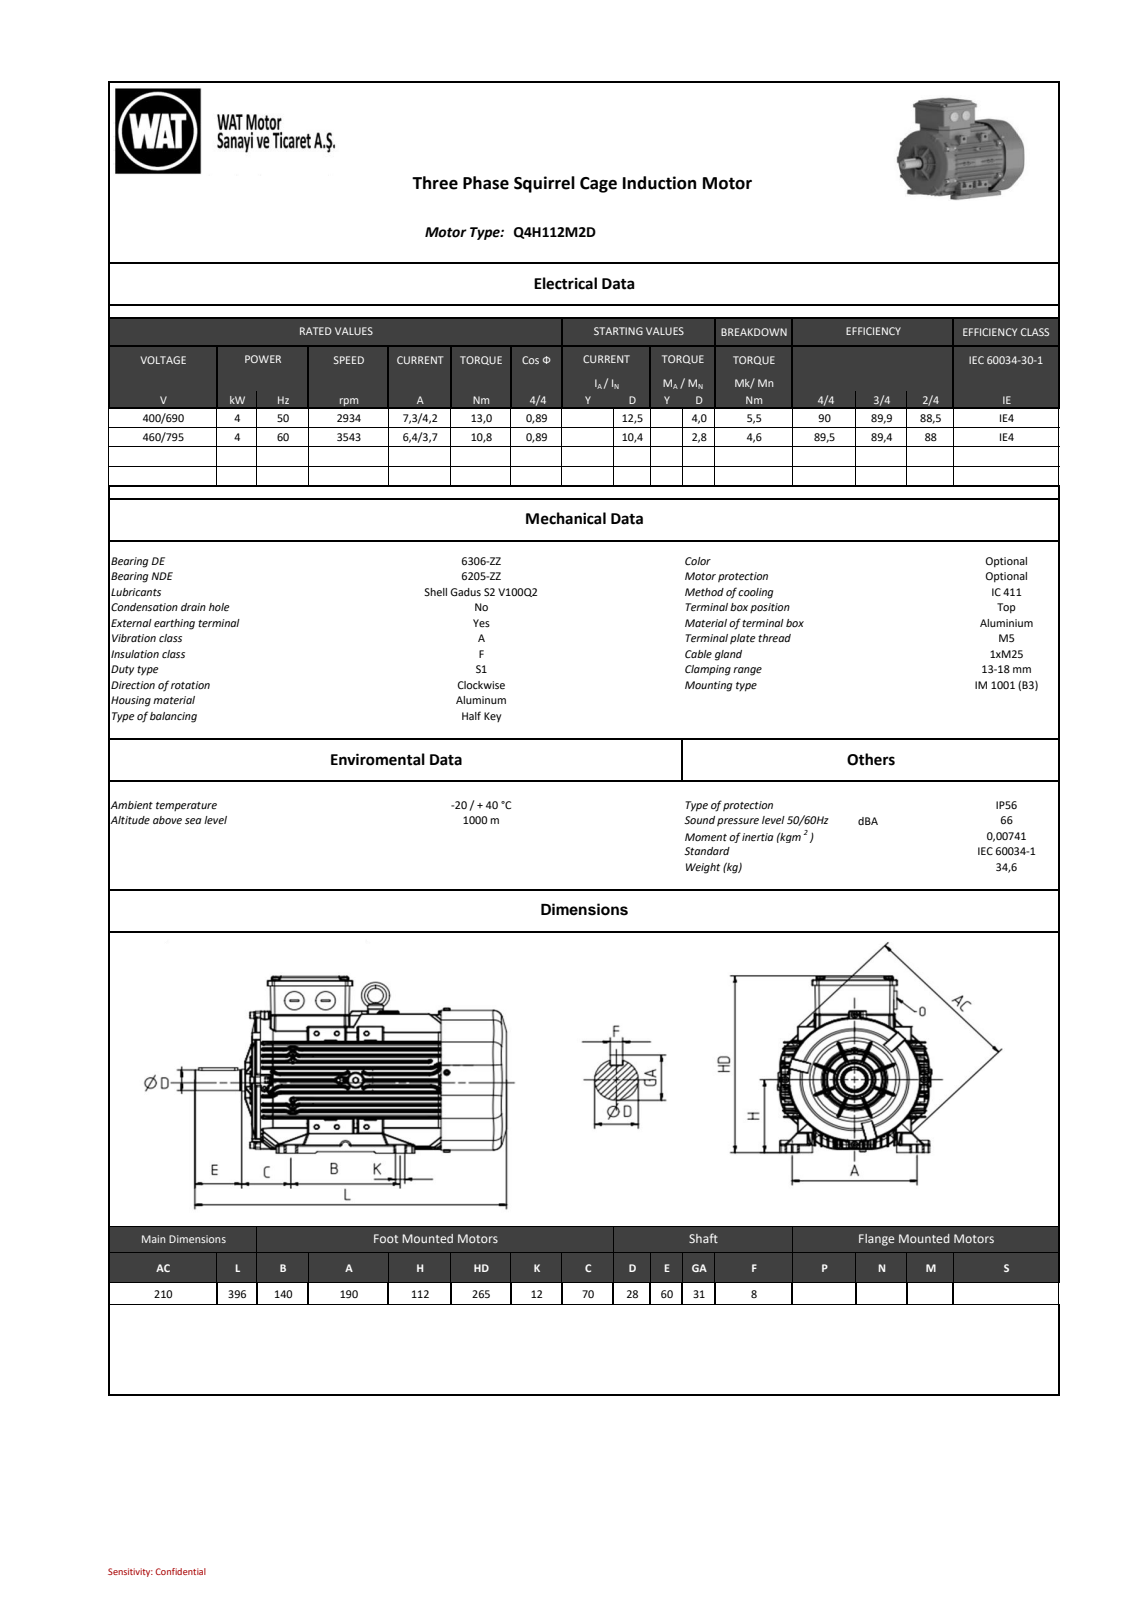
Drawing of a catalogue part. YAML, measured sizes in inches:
part_name: "QH series_ 112_B3_stp_objects"
step_written_by: "SIEMENS PLM Software NX2206.8101 (AUTOMOTIVE_DESIGN)"
units: inches
bodies: {solids: 0, faces: 6868, planar: 1512, cylindrical: 2655, other: 2701}
overall_size: [15.591, 10.807, 8.863]
round_holes:
  - {diameter: 0.181, count: 2}
  - {diameter: 0.315, count: 1}
  - {diameter: 0.335, count: 1}
round_bosses_or_shafts:
  - {diameter: 0.394, count: 4}
  - {diameter: 0.315, count: 4}
  - {diameter: 0.984, count: 2}
  - {diameter: 7.402, count: 1}
  - {diameter: 1.411, count: 1}
  - {diameter: 1.181, count: 1}
  - {diameter: 1.161, count: 1}
  - {diameter: 1.15, count: 1}
partial_cylinders:
  - {radius: 0.031, count: 577}
  - {radius: 0.079, count: 562}
  - {radius: 0.039, count: 347}
  - {radius: 0.02, count: 298}
  - {radius: 0.118, count: 80}
  - {radius: 0.157, count: 12}
  - {radius: 0.236, count: 12}
  - {radius: 0.394, count: 10}
face_to_face_distances: [0.039, 0.846, 0.433, 1.416, 3.919, 0.983, 0.321, 4.444, 3.538, 3.56]
